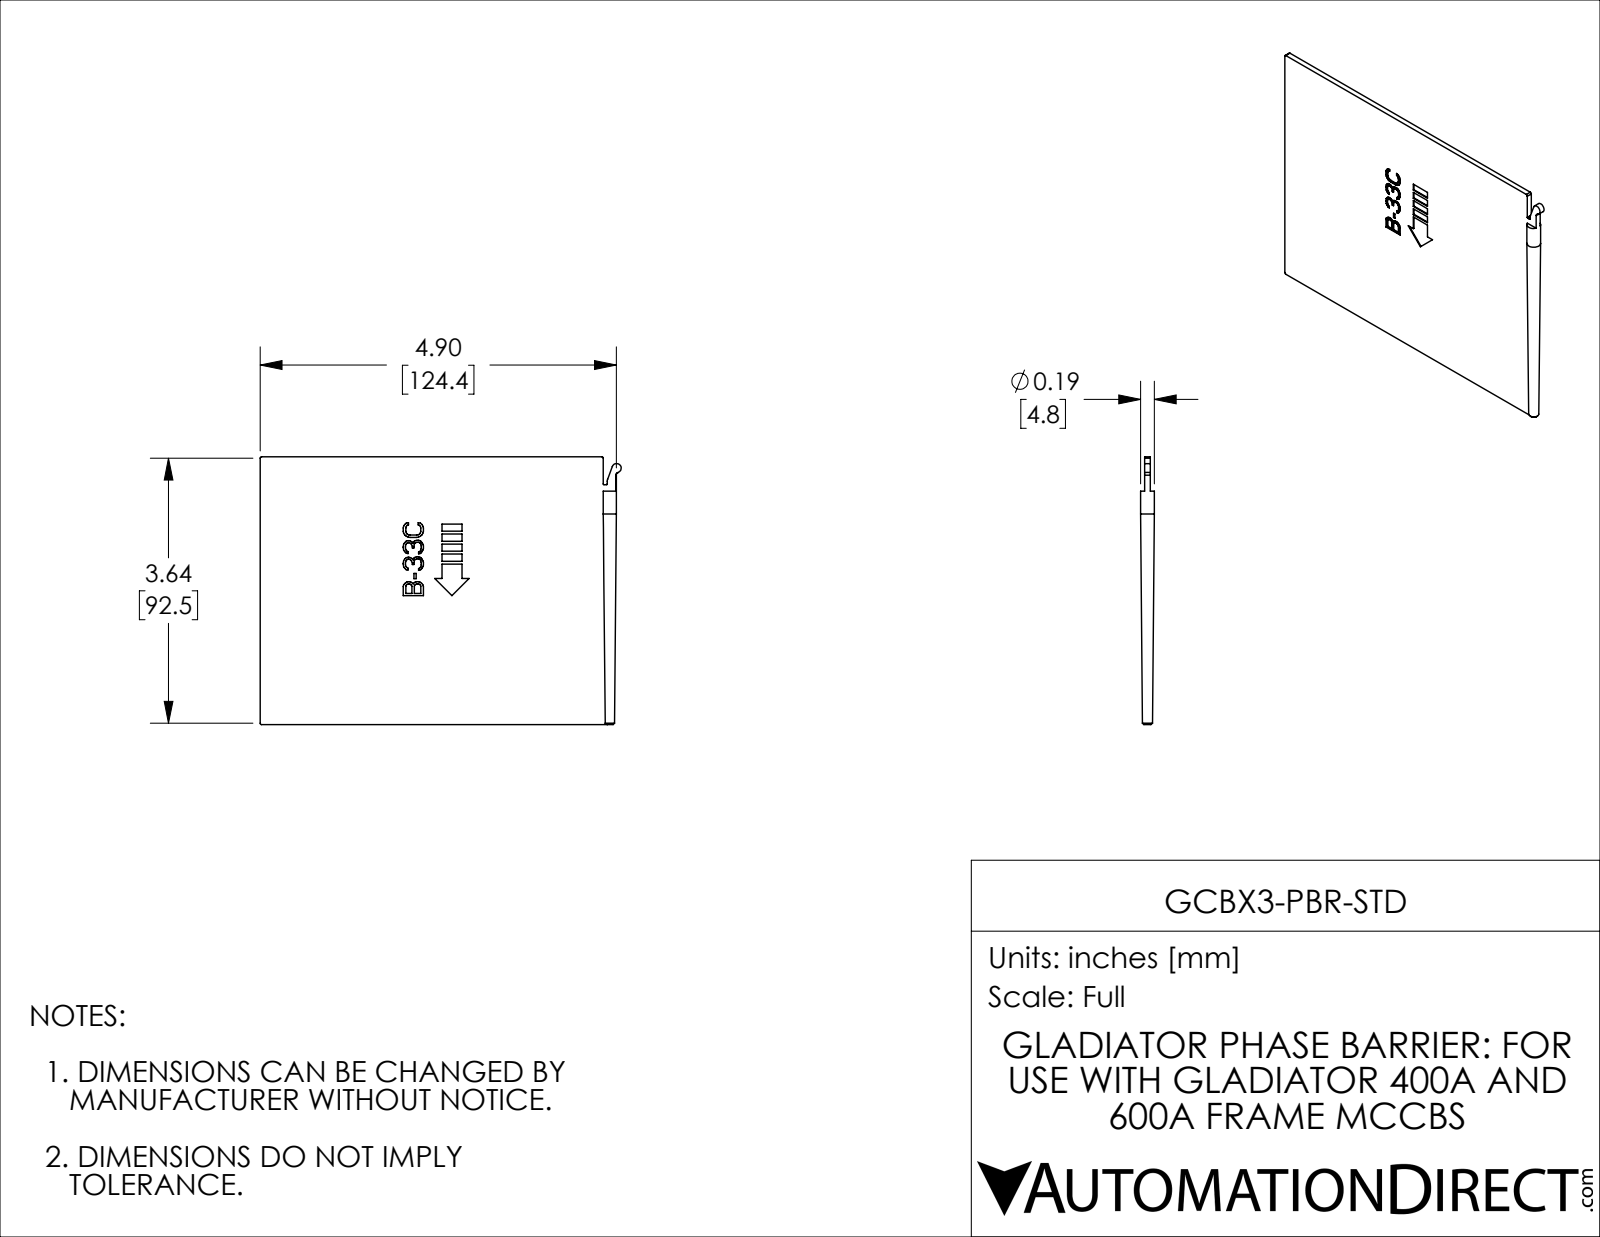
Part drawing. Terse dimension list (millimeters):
name: GCBX3-PBR-STD
written by: SolidWorks 2021 (CONFIG_CONTROL_DESIGN)
unit: mm
bodies: 1 solid, 492 faces (475 planar, 10 cylindrical, 7 other)
size: 126.1 × 93.5 × 4.8
volume: 23 520 mm³; area: 24 330 mm²
bosses: 1× ⌀4.8
rounds: 3× R0.5, 2× R0.3, 1× R1.6, 1× R2
face distances: 2, 1.7, 93.5, 1.4, 7, 3.5, 119.8, 6, 1, 2.5
